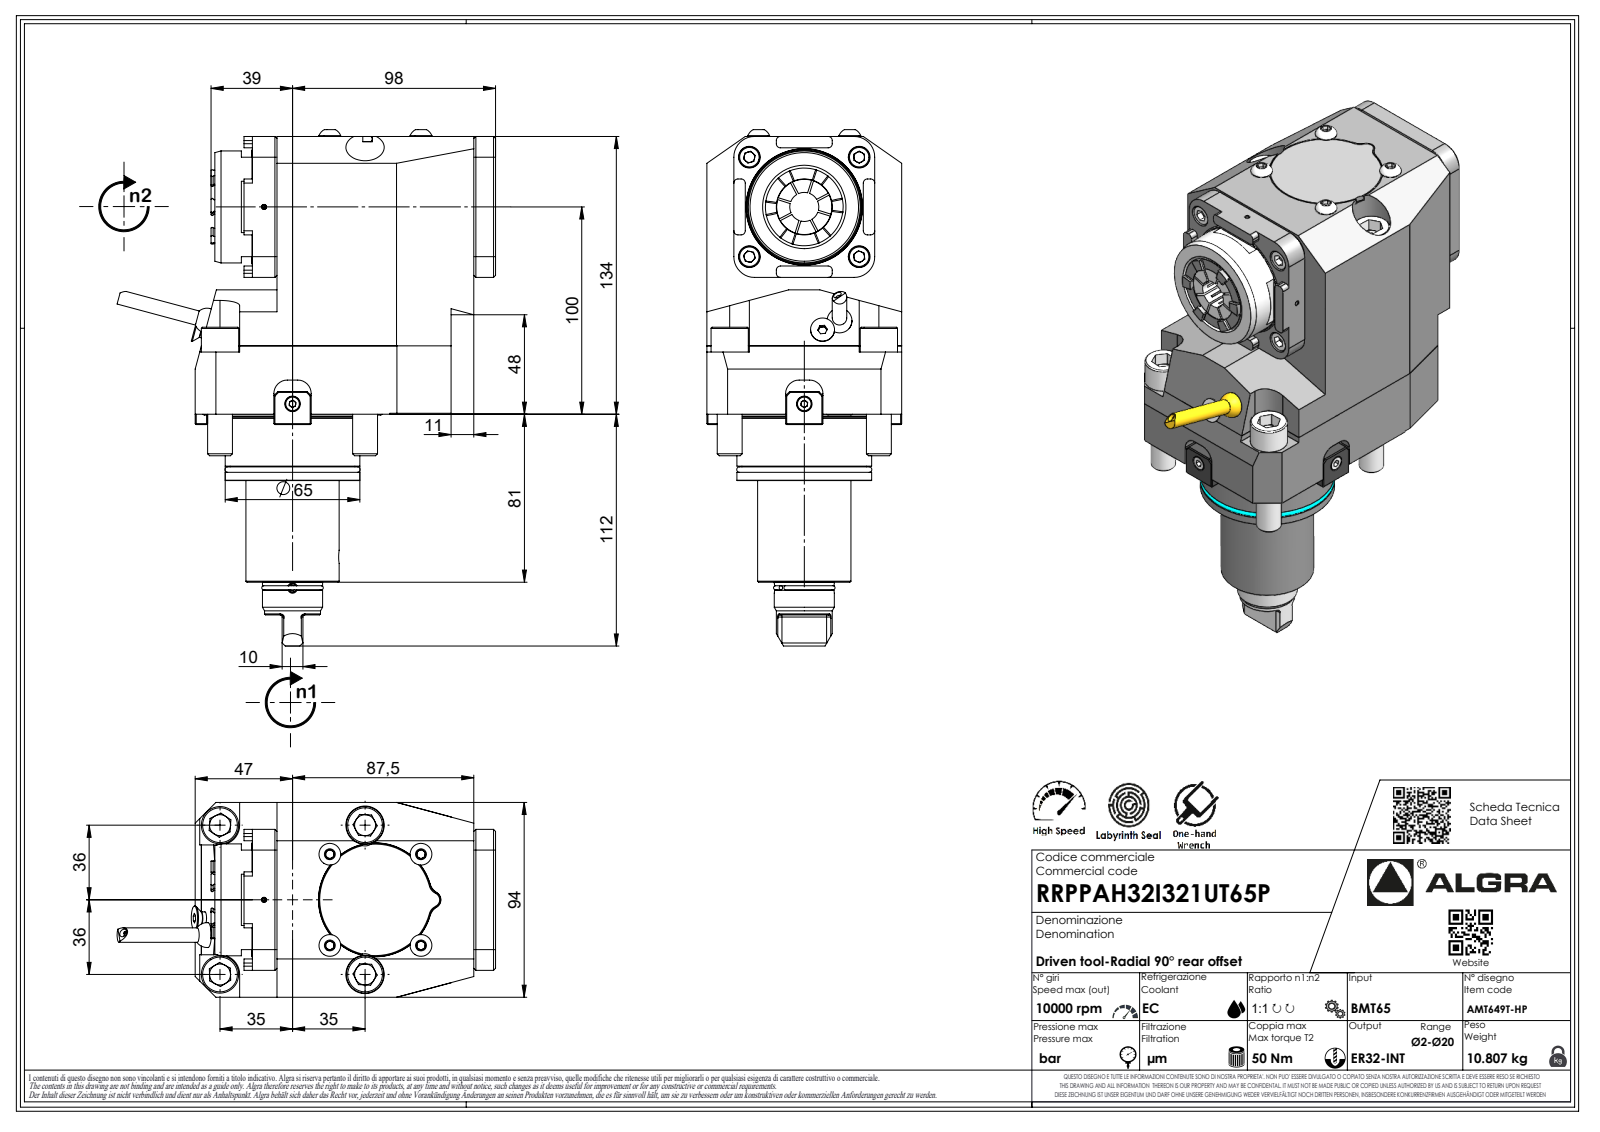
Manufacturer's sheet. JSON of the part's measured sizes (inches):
{"part_name": "RRPPAH32I321UT65P", "step_written_by": "SolidWorks 2023 (AUTOMOTIVE_DESIGN)", "units": "inches", "bodies": {"solids": 1, "faces": 606, "planar": 400, "cylindrical": 80, "other": 126}, "overall_size": [9.677, 7.191, 3.701], "volume_in3": 98.92, "surface_area_in2": 164.8, "round_holes": [[0.083, 1]], "round_bosses_or_shafts": [[0.472, 4], [0.709, 2], [2.559, 1], [2.543, 1], [2.37, 1], [2.126, 1], [1.772, 1], [1.142, 1]], "partial_cylinders_radius": [[0.079, 16], [0.013, 7], [0.02, 7], [0.146, 7], [0.039, 6], [0.394, 4], [0.374, 2], [0.906, 2]], "face_to_face_distances": [3.701, 5.276, 0.846, 3.189, 5.256, 1.181, 0.02, 3.307, 4.154, 4.488]}
